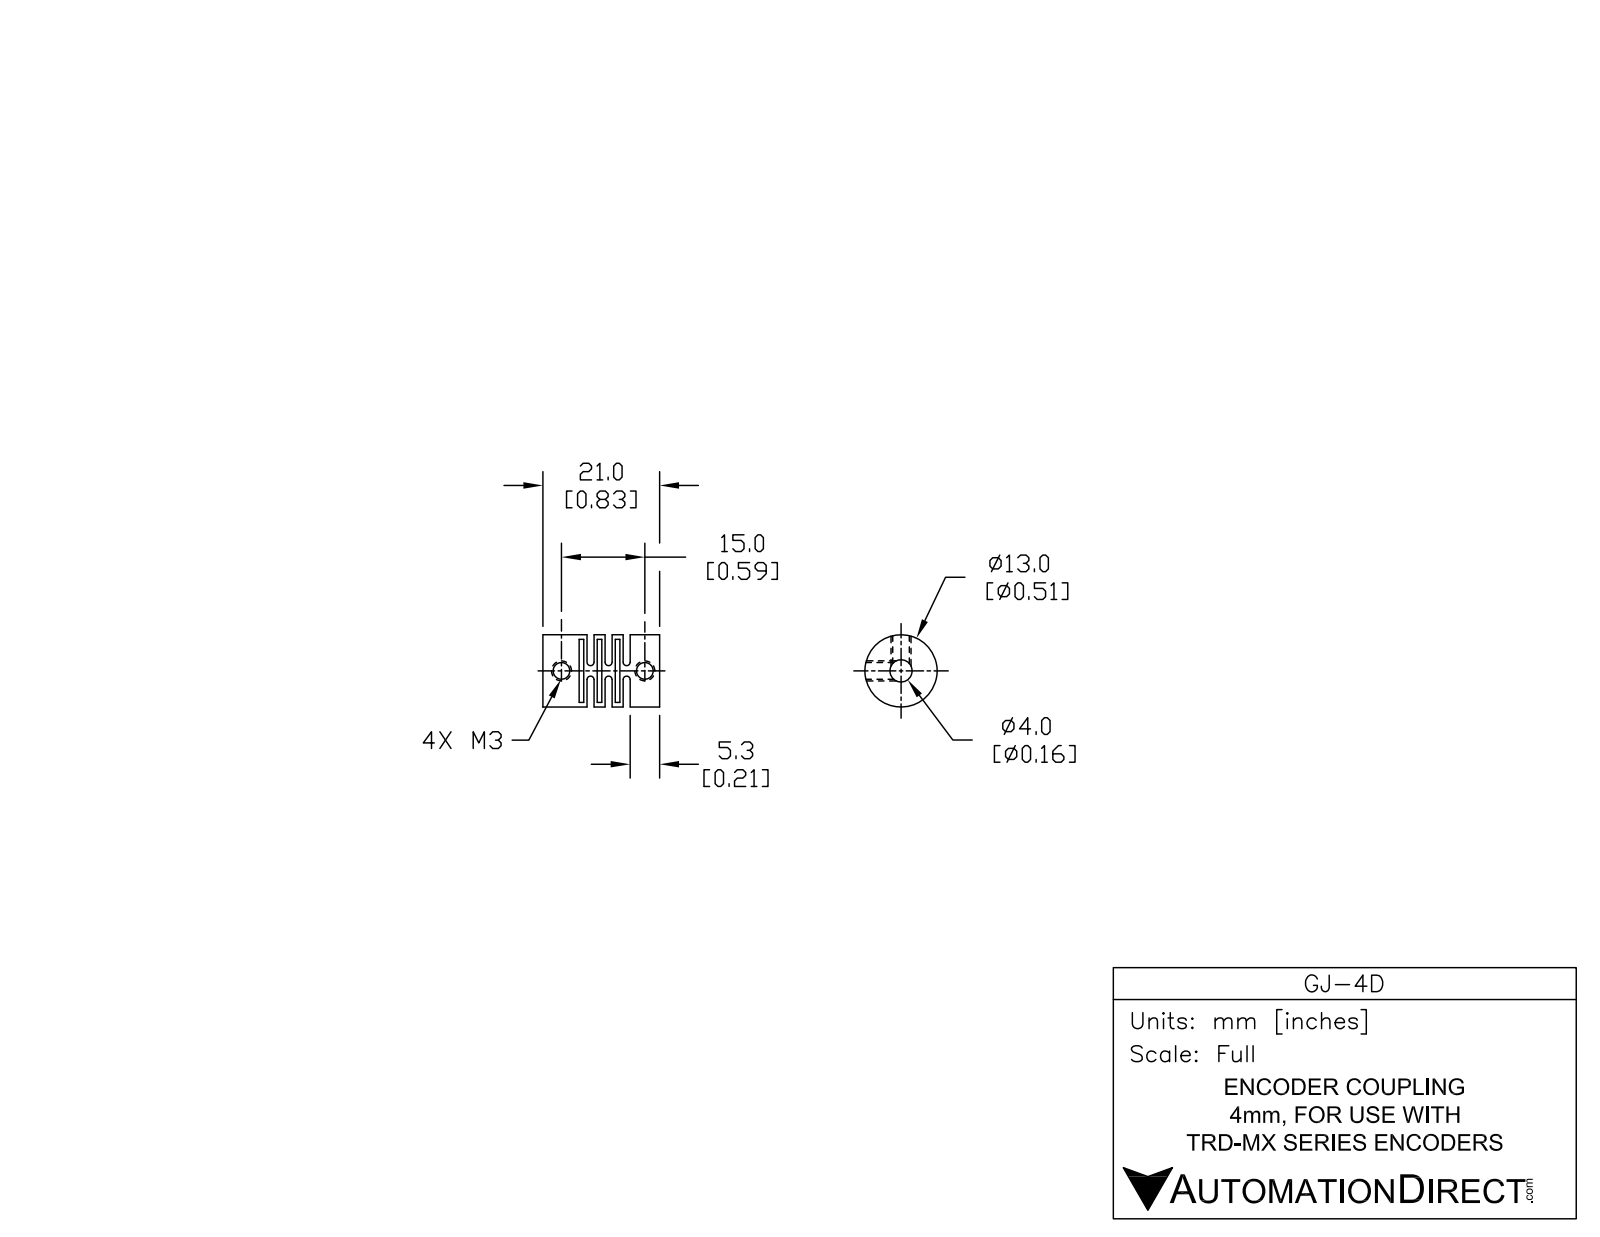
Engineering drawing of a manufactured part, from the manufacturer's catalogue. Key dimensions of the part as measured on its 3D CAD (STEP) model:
Part name (STEP PRODUCT): GJ-4D
STEP written by: SolidWorks 2016 (AUTOMOTIVE_DESIGN)
Units: millimetres
Bodies: 1 solid, 143 faces (94 planar, 19 cylindrical, 30 other)
Overall size (bounding box): 21 × 13 × 13
Volume: 1 964 mm³ · Surface area: 2 376 mm²
Round holes (diameter × count): ⌀2.5 ×4, ⌀4 ×1
Round bosses / shafts (diameter × count): ⌀13 ×1
Partial cylindrical surfaces — rounded edges, fillets, slot ends (radius × count): R1.5 ×2
Main face-to-face distances: 2.3, 1, 4.6, 4.8, 3.3, 7.1, 1.3, 2.5, 5.3, 6.3
Hole centre spacings: 15.4
